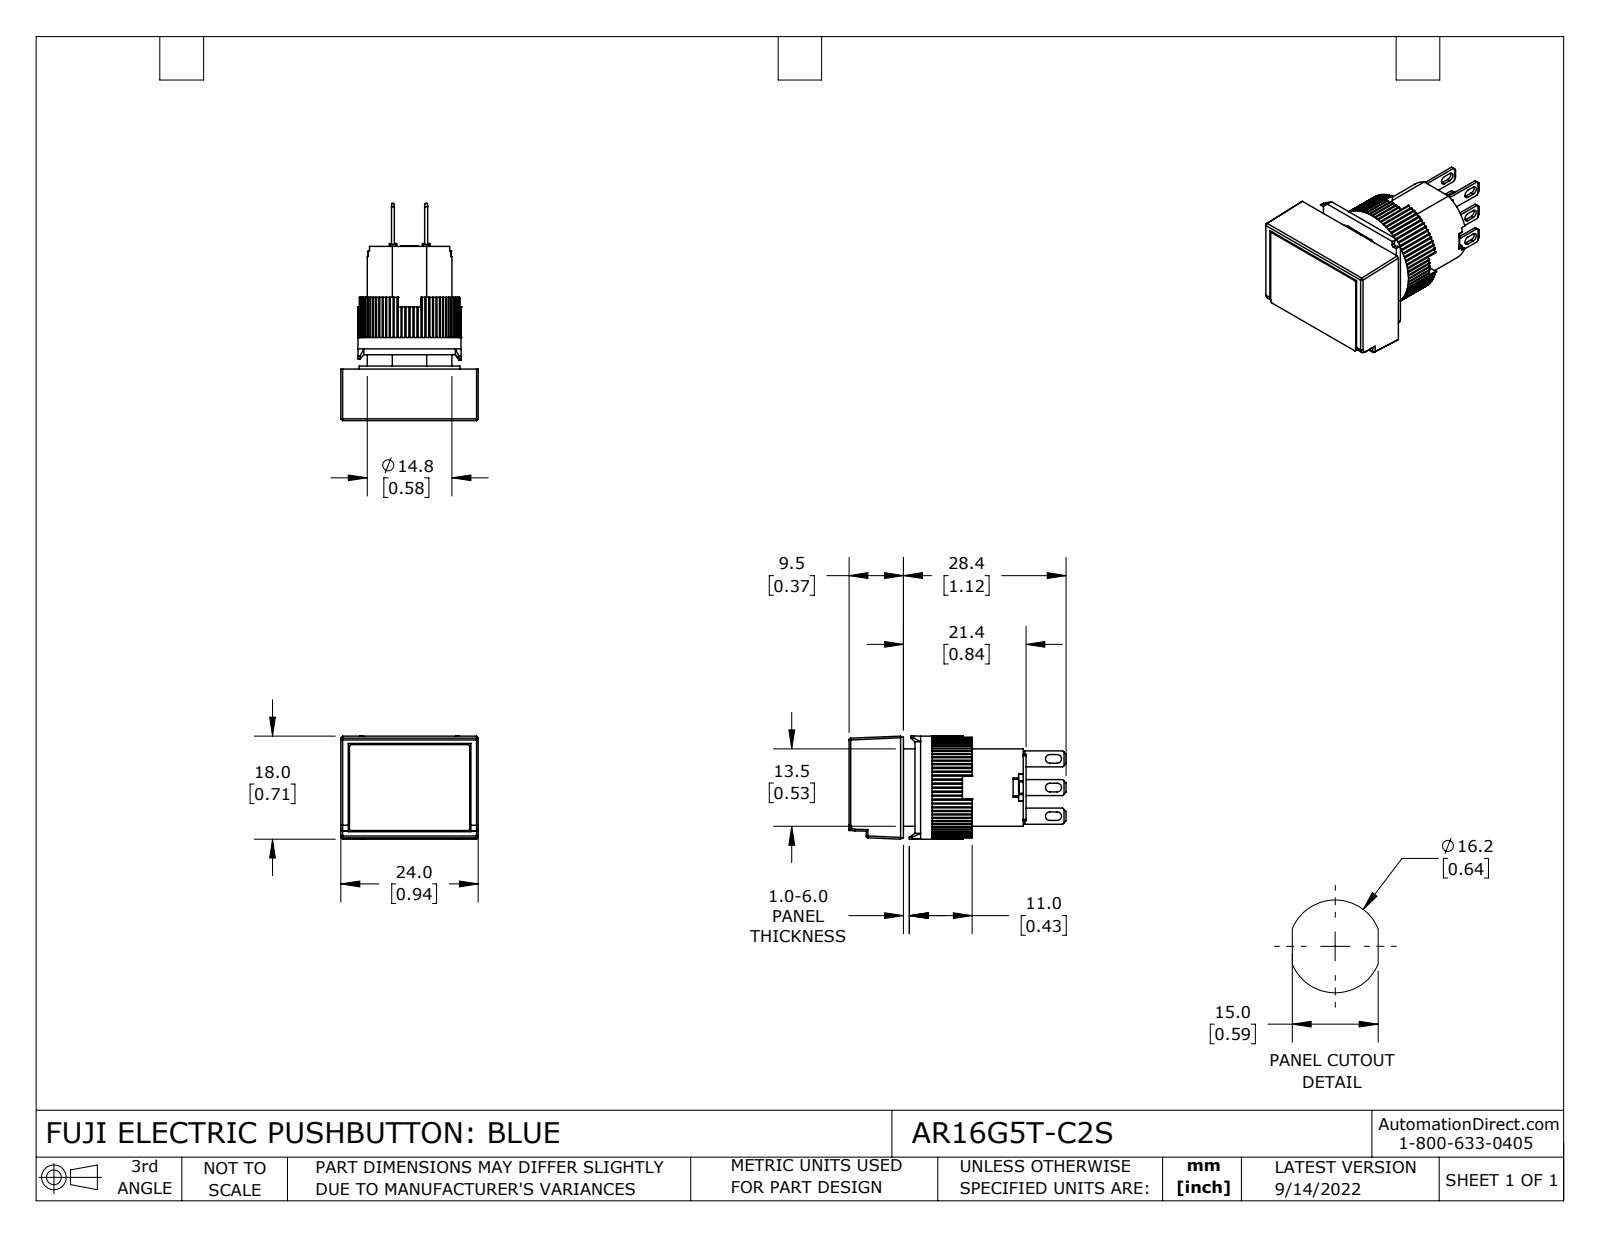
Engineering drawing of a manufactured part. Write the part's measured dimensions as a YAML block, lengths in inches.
part_name: "AR16G5T-C2S"
step_written_by: "SolidWorks 2021 (CONFIG_CONTROL_DESIGN)"
units: inches
bodies: {solids: 12, faces: 811, planar: 630, cylindrical: 175, other: 6}
overall_size: [1.492, 0.945, 0.709]
volume: 0.447
surface_area: 9.321
round_holes:
  - {diameter: 0.543, count: 1}
  - {diameter: 0.583, count: 1}
round_bosses_or_shafts:
  - {diameter: 0.709, count: 1}
  - {diameter: 0.693, count: 1}
partial_cylinders:
  - {radius: 0.01, count: 80}
  - {radius: 0.008, count: 12}
  - {radius: 0.012, count: 6}
  - {radius: 0.03, count: 6}
  - {radius: 0.039, count: 1}
face_to_face_distances: [0.213, 0.354, 0.142, 0.492, 0.35, 0.138, 0.02, 0.843, 0.059, 0.453]
